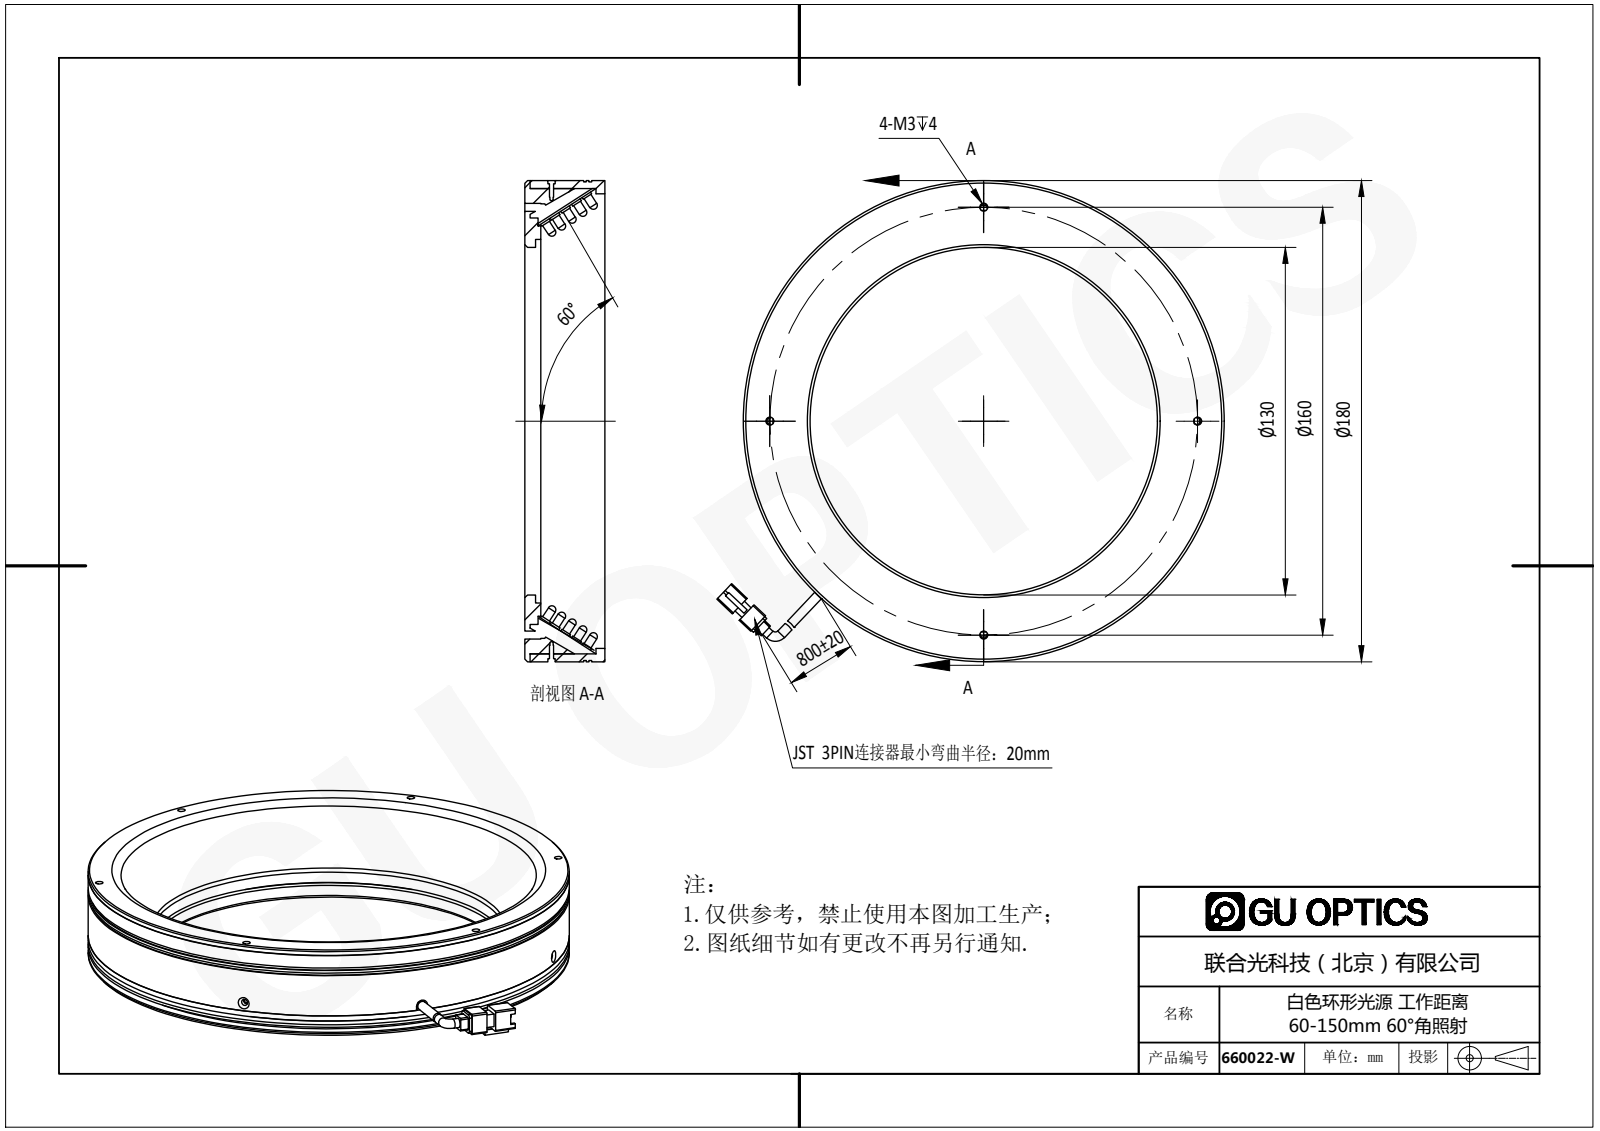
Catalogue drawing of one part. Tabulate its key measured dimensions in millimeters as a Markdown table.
| quantity | value |
| --- | --- |
| part name | 660022-W |
| STEP written by | SolidWorks 2016 (AUTOMOTIVE_DESIGN) |
| units | millimeters |
| bodies | 506 solids, 8844 faces (6099 planar, 2169 cylindrical, 576 other) |
| overall size | 189.81 × 180 × 34 |
| volume | 204 941 mm³ |
| surface area | 199 276 mm² |
| round holes (diameter × count) | 1.6 × 8, 1.25 × 6, 1.5 × 6, 2.8 × 6, 3.5 × 5, 2.5 × 4, 3 × 4, 2.4 × 2, 130 × 1, 131 × 1, 136 × 1, 170 × 1 |
| round bosses / shafts (diameter × count) | 3.8 × 500, 3 × 500, 3.5 × 2, 180 × 1, 179 × 1, 174 × 1, 172 × 1, 151.08 × 1 |
| partial cylindrical surfaces (radius × count) | 0.5 × 12, 1 × 4, 1.75 × 1, 6 × 1 |
| main face-to-face distances | 2, 1, 3.5, 4.5, 32, 26, 1.5, 2.5, 30.5, 3 |
| hole center spacings | 87, 150.69, 168.07, 43.75, 45.04, 83.72, 118.19, 144.67 |
